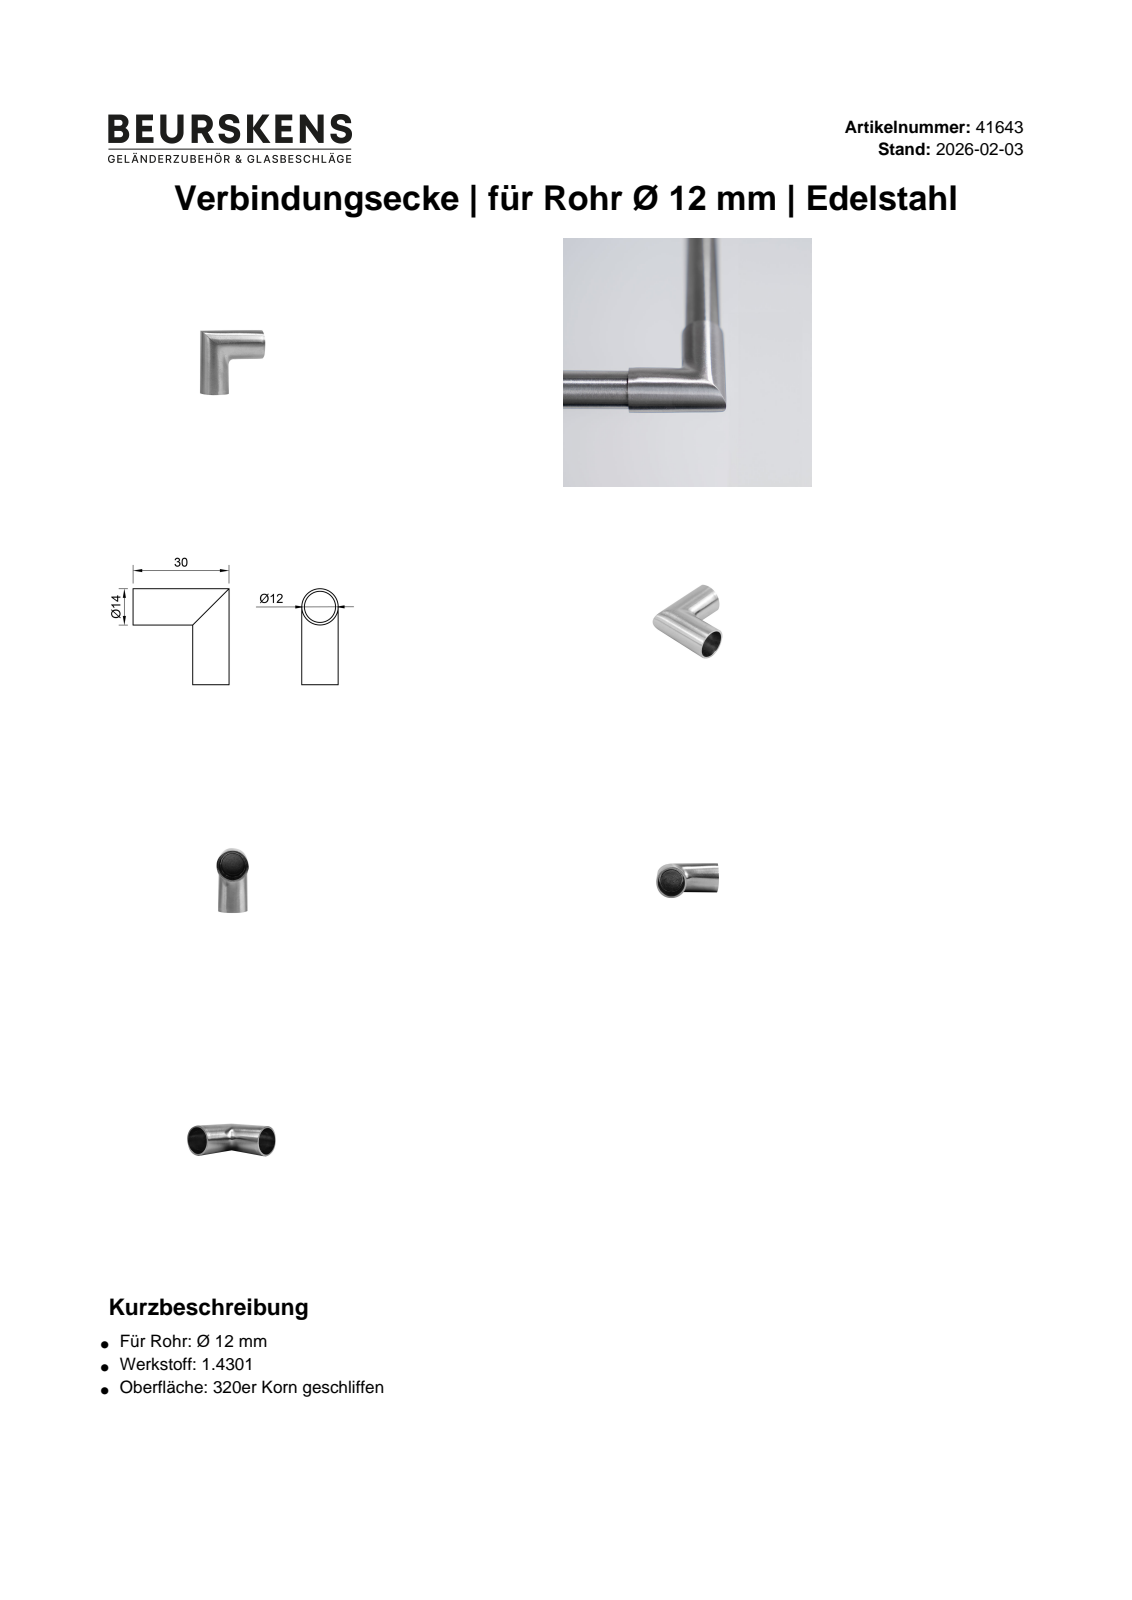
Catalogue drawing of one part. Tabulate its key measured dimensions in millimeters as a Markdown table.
| quantity | value |
| --- | --- |
| part name | 41643 |
| STEP written by | Autodesk Inventor 2022 (AUTOMOTIVE_DESIGN) |
| units | millimeters |
| bodies | 1 solid, 8 faces (2 planar, 4 cylindrical, 2 other) |
| overall size | 37 × 37 × 14 |
| volume | 5 798 mm³ |
| surface area | 4 040 mm² |
| round holes (diameter × count) | 12 × 2 |
| round bosses / shafts (diameter × count) | 14 × 2 |
